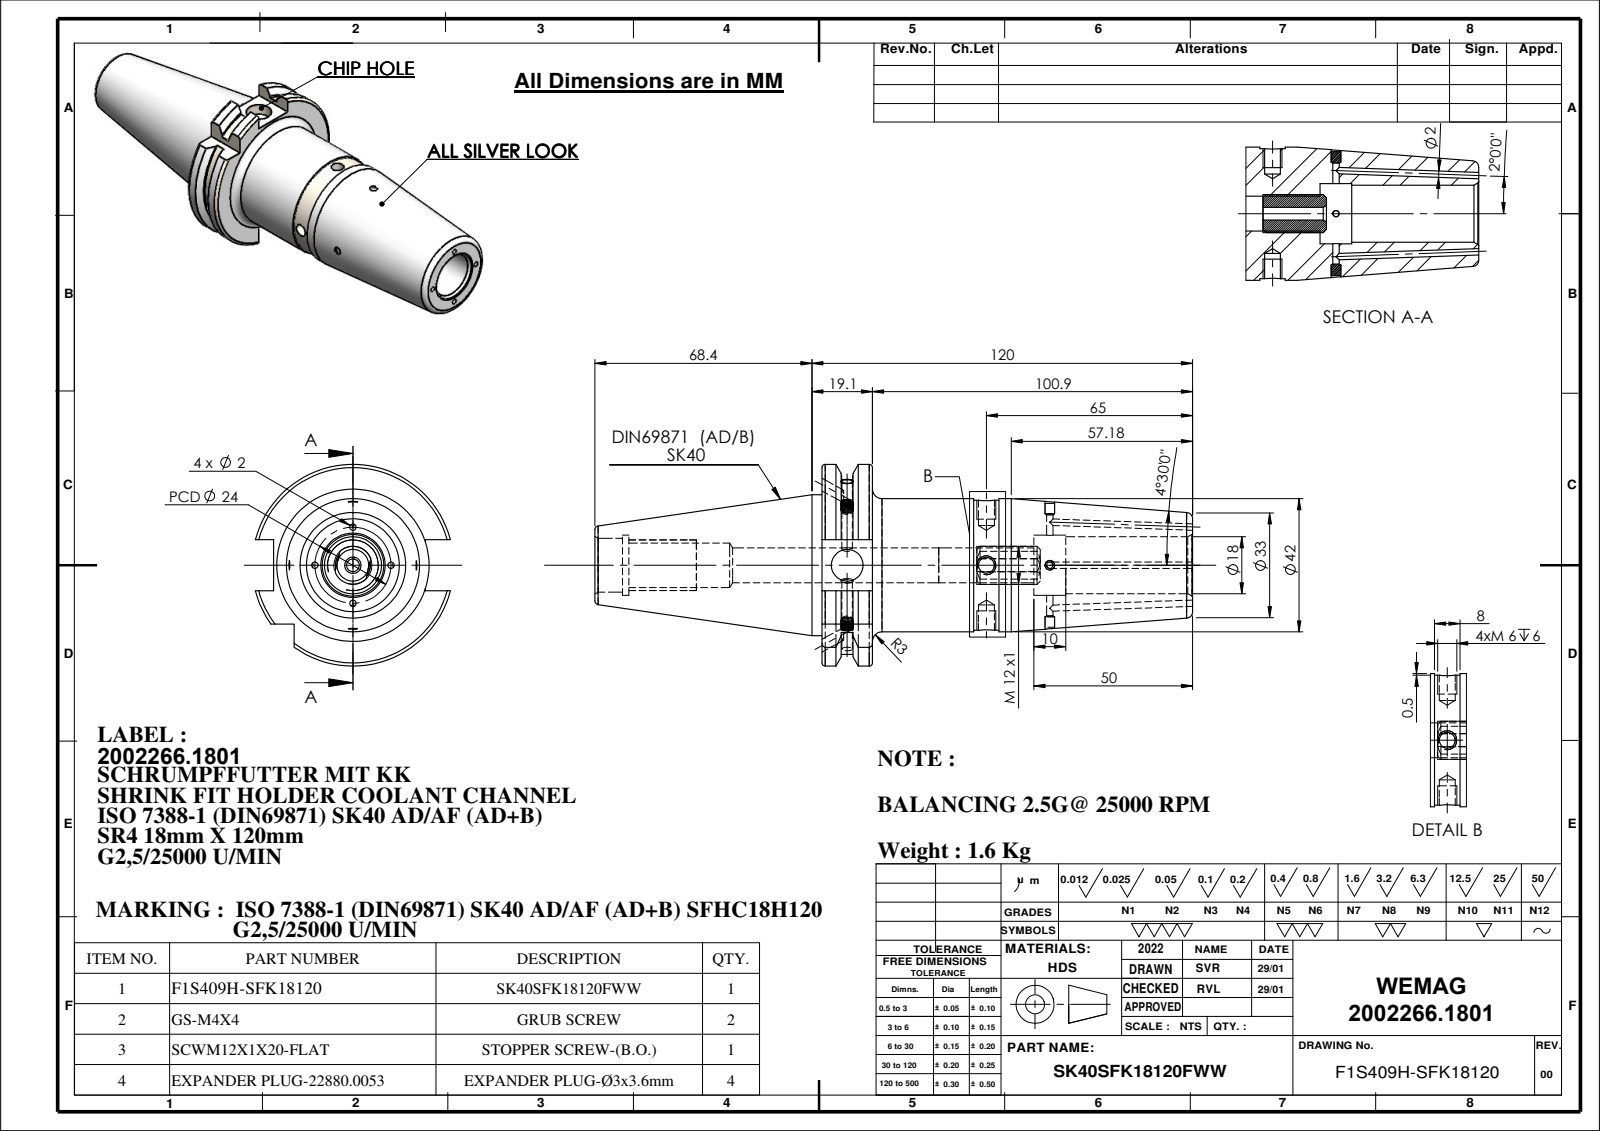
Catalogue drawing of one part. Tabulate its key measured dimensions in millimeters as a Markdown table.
| quantity | value |
| --- | --- |
| part name | SCWM12X1X20-FLAT; EXPANDER PLUG Ø3x3.6; SK40SFK18120FWW; 91406-SR418120 (+1 more) |
| STEP written by | SolidWorks 2018 (CONFIG_CONTROL_DESIGN) |
| units | millimeters |
| bodies | 8 solids, 304 faces (63 planar, 113 cylindrical, 128 other) |
| overall size | 188.4 × 63.55 × 61.48 |
| volume | 207 296 mm³ |
| surface area | 40 876 mm² |
| round holes (diameter × count) | 2 × 6, 3 × 2, 5 × 2, 3.3 × 1, 4 × 1, 10 × 1, 10.99 × 1, 11 × 1, 14 × 1, 17 × 1, 17.99 × 1, 18.99 × 1 |
| round bosses / shafts (diameter × count) | 4 × 2, 44.45 × 1, 42 × 1, 41 × 1 |
| partial cylindrical surfaces (radius × count) | 6 × 1, 28.12 × 1, 31.77 × 1 |
| main face-to-face distances | 15.9, 116.8, 100.9, 47.8, 66.8, 50.9, 50, 16.1, 60.9, 76.8 |
| hole center spacings | 20, 43.85, 63.85 |
